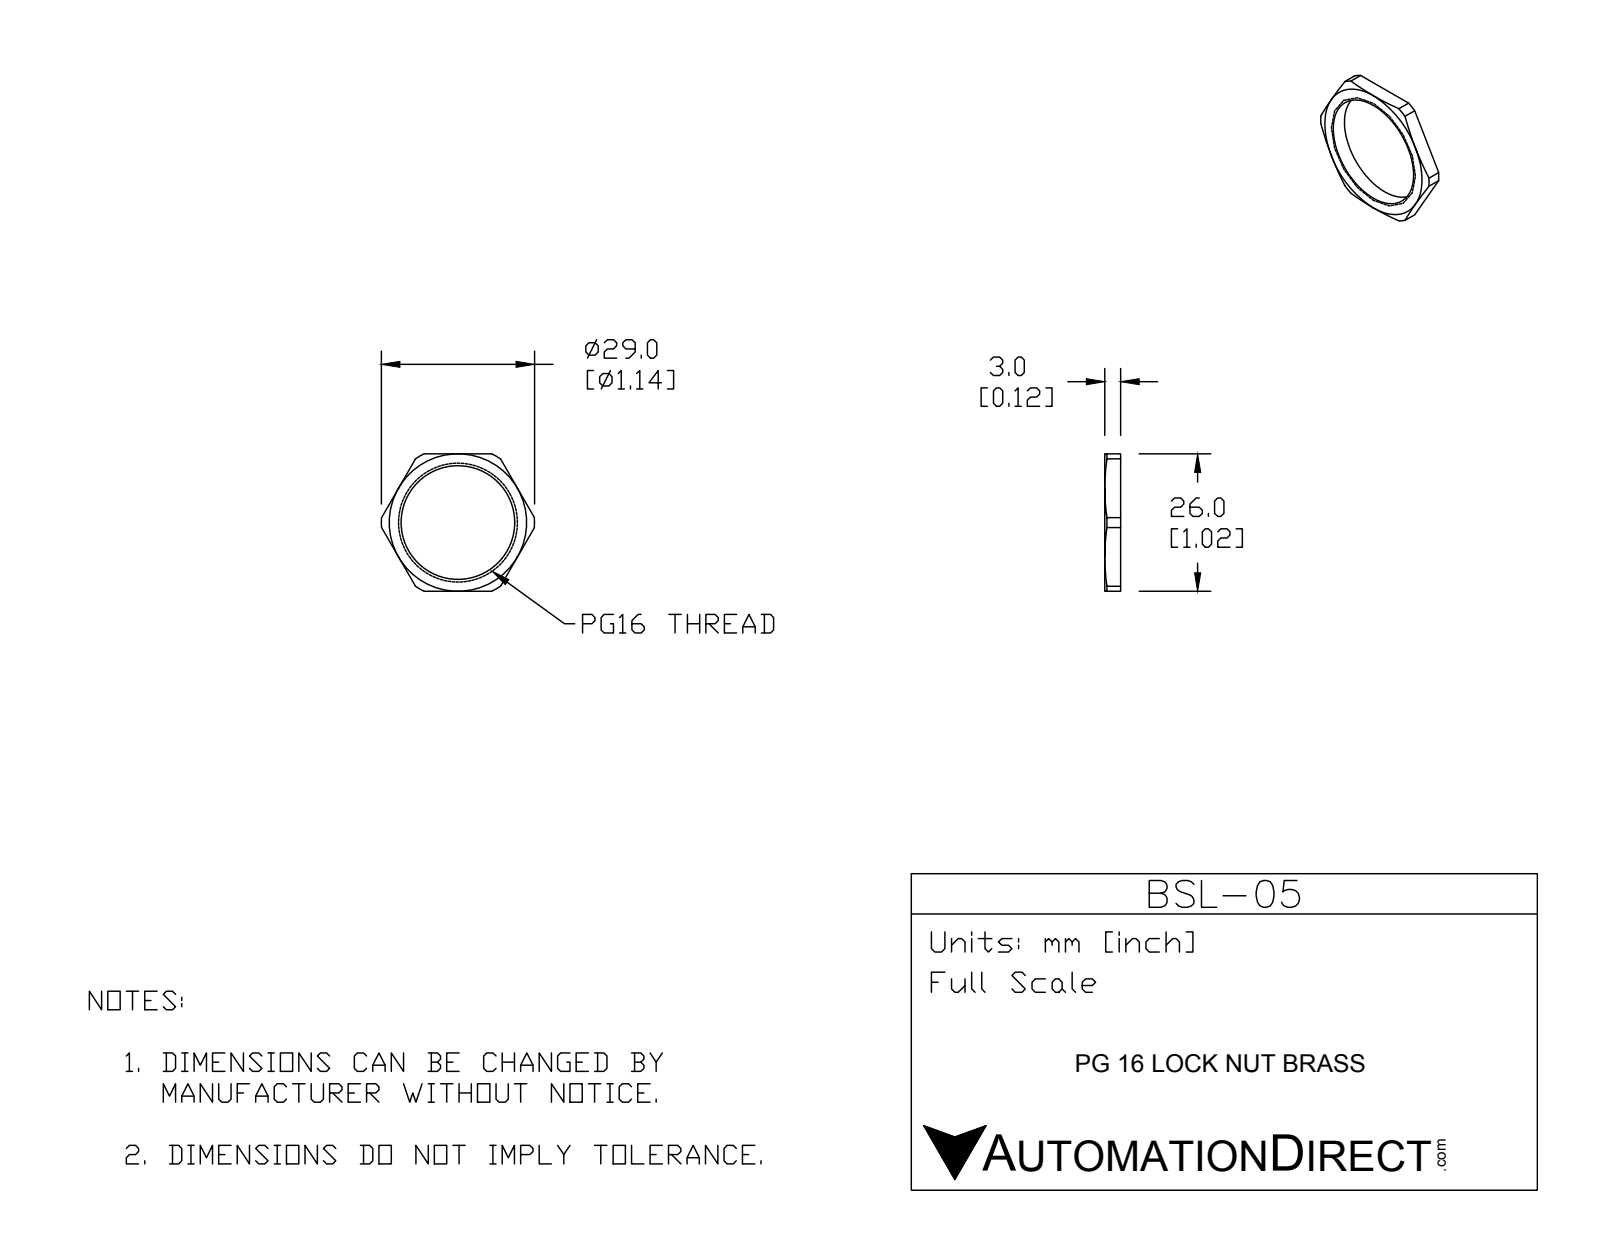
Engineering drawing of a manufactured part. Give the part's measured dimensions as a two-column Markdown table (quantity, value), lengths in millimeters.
| quantity | value |
| --- | --- |
| part name | BSL-05 |
| STEP written by | SolidWorks 2015 (CONFIG_CONTROL_DESIGN) |
| units | millimeters |
| bodies | 1 solid, 23 faces (8 planar, 9 cylindrical, 6 other) |
| overall size | 29 × 26 × 3 |
| volume | 651 mm³ |
| surface area | 893 mm² |
| round holes (diameter × count) | 21.5 × 1 |
| partial cylindrical surfaces (radius × count) | 14.5 × 1 |
| main face-to-face distances | 3, 26 |
